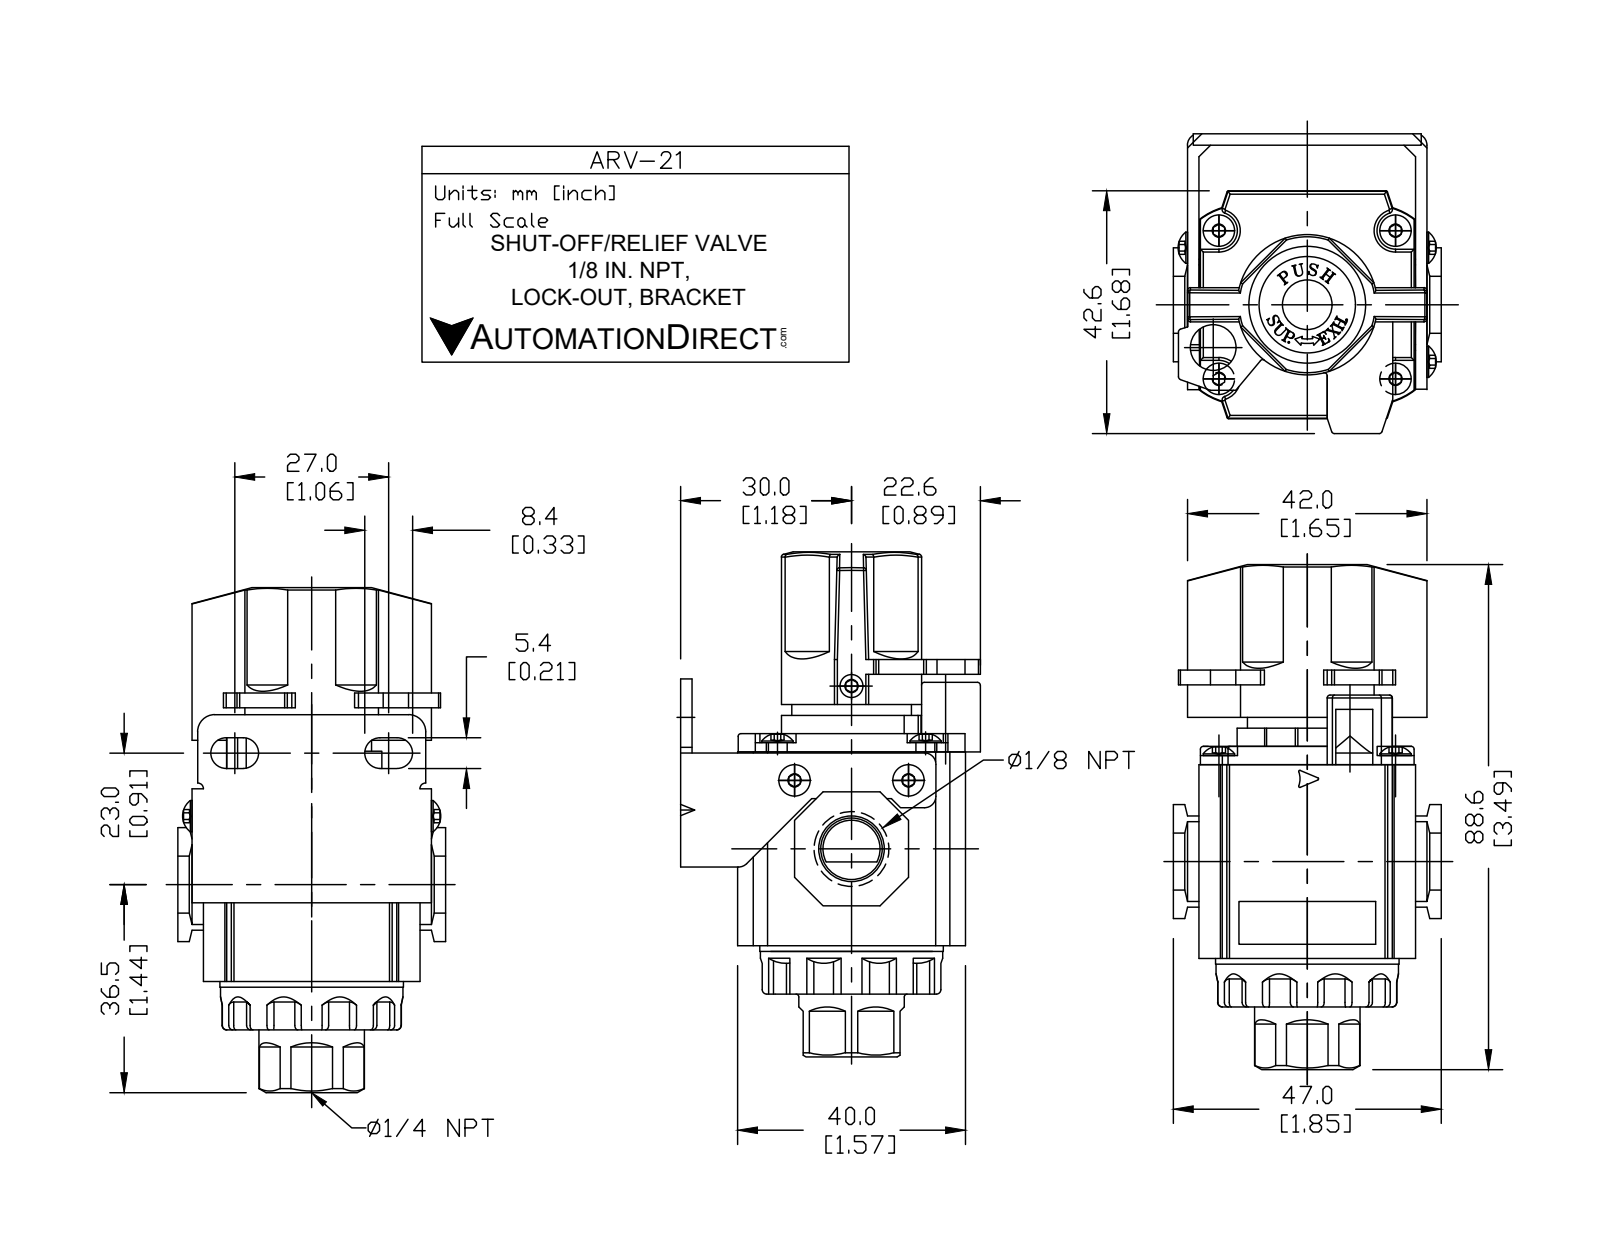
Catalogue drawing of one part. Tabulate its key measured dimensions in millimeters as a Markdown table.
| quantity | value |
| --- | --- |
| part name | ARV-21 |
| STEP written by | SolidWorks 2015 (CONFIG_CONTROL_DESIGN) |
| units | millimeters |
| bodies | 18 solids, 396 faces (284 planar, 75 cylindrical, 37 other) |
| overall size | 89 × 52.6 × 47 |
| volume | 87 512 mm³ |
| surface area | 28 244 mm² |
| round holes (diameter × count) | 8 × 1, 8.43 × 1, 17.22 × 1 |
| round bosses / shafts (diameter × count) | 5.5 × 4, 31.5 × 1, 30.87 × 1, 24.6 × 1, 18.7 × 1, 12.3 × 1 |
| partial cylindrical surfaces (radius × count) | 1.5 × 6, 2.7 × 4, 3.85 × 4, 1 × 2, 2 × 2, 3 × 2, 5 × 1, 9.18 × 1 |
| main face-to-face distances | 2, 40, 34, 37.2, 3.2, 38, 10, 17, 8, 42.5 |
| hole center spacings | 18.12 |
